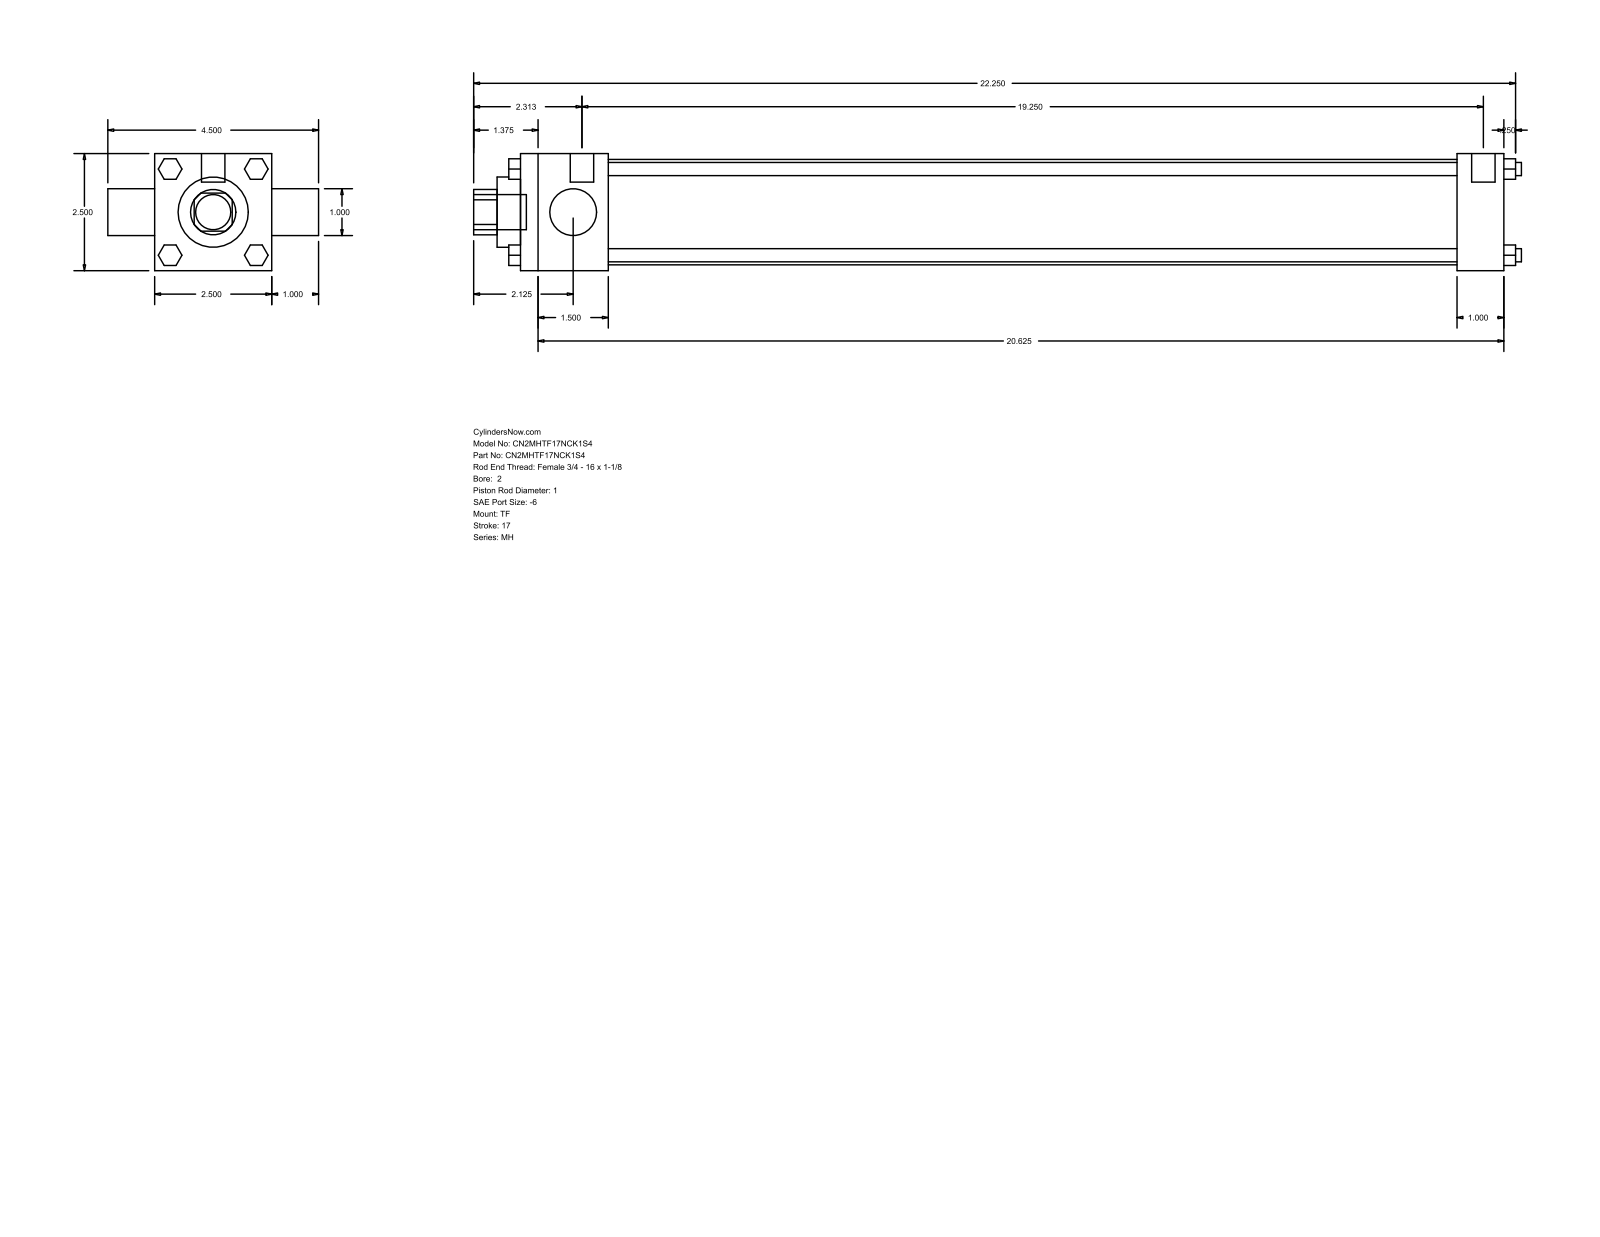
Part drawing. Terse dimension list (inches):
name: MH_TF__0200_1
written by: GSSL Pune (CONFIG_CONTROL_DESIGN)
unit: in
bodies: 0 solids, 120 faces (92 planar, 28 cylindrical, 0 other)
size: 22.375 × 4.5 × 2.5
holes: 2× ⌀1, 1× ⌀1.5, 1× ⌀2.25
bosses: 4× ⌀0.281, 3× ⌀0.219, 2× ⌀0.5, 1× ⌀0.75
rounds: 1× R0.484
face distances: 2.5, 21, 1, 1.875, 20, 18.125, 19.125, 3.5, 21.5, 0.25
